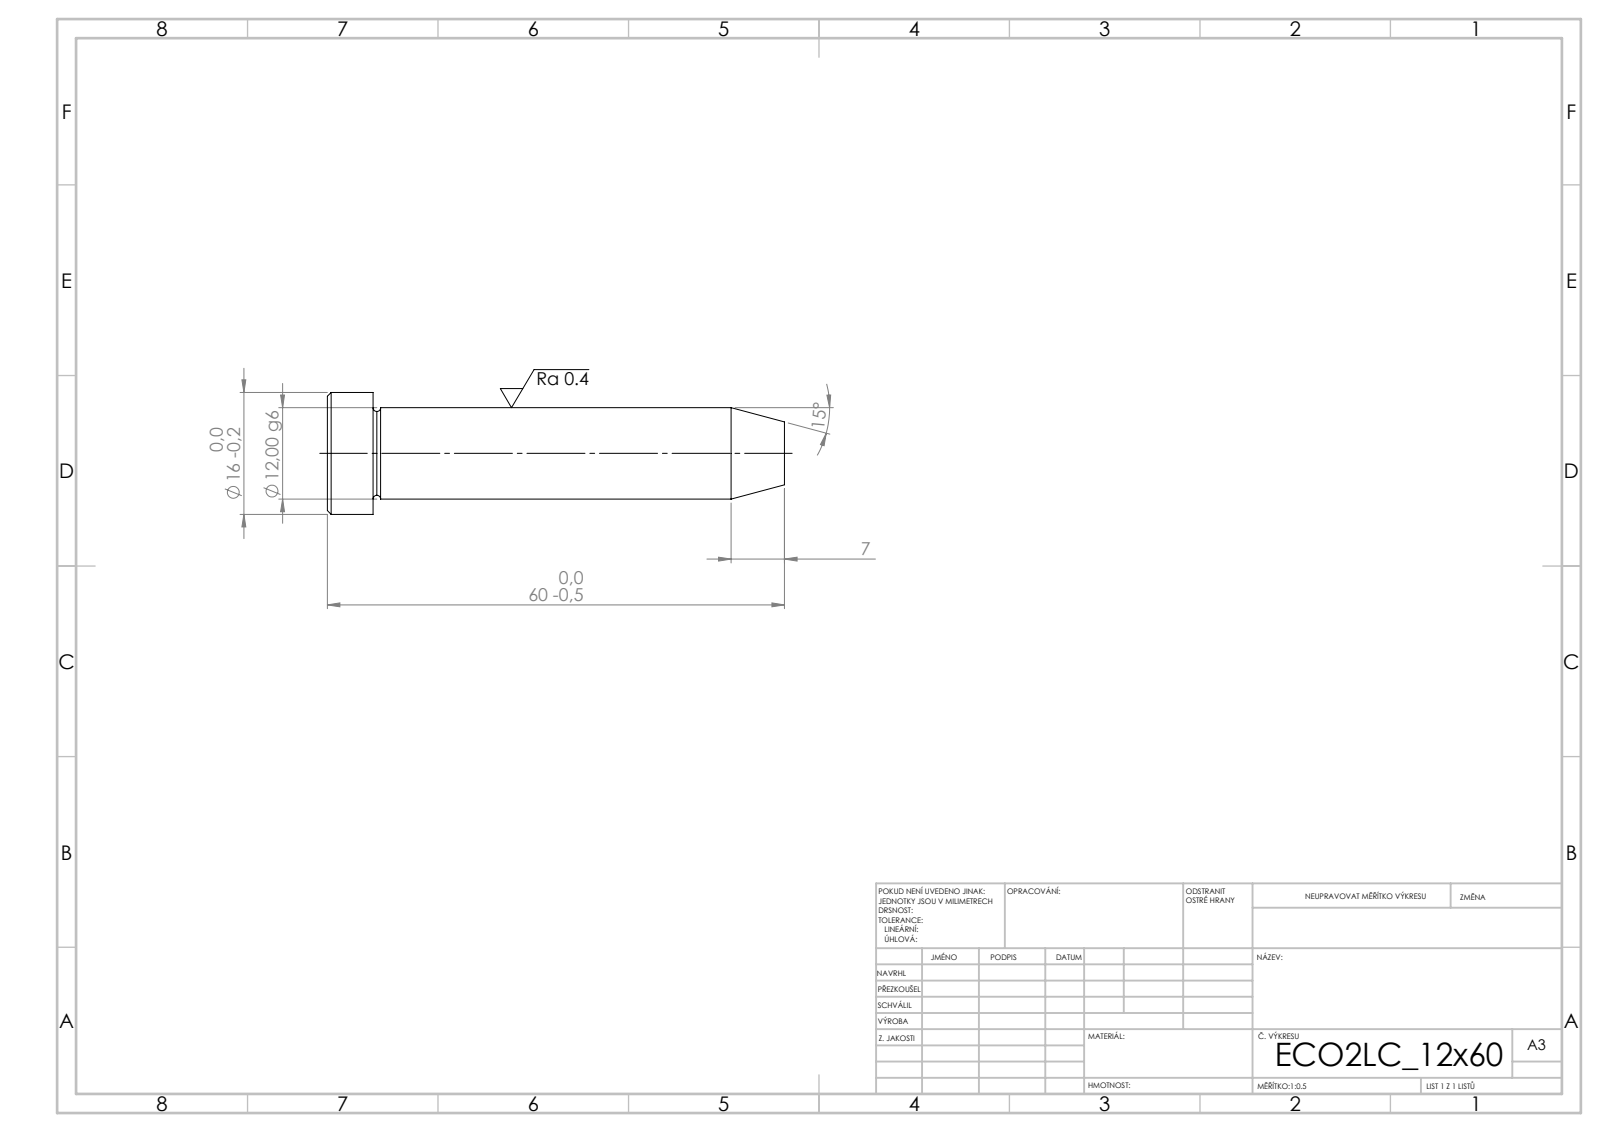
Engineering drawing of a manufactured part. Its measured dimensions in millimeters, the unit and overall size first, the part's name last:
Units: millimetres
Overall size (bounding box): 60 × 16 × 16
Round bosses / shafts (diameter × count): ⌀16 ×1, ⌀12 ×1
Main face-to-face distances: 6, 54, 60
Volume: 7 071 mm³ · Surface area: 2 650 mm²
Bodies: 1 solid, 15 faces (3 planar, 4 cylindrical, 8 other)
STEP written by: SolidWorks 2019 (CONFIG_CONTROL_DESIGN)
